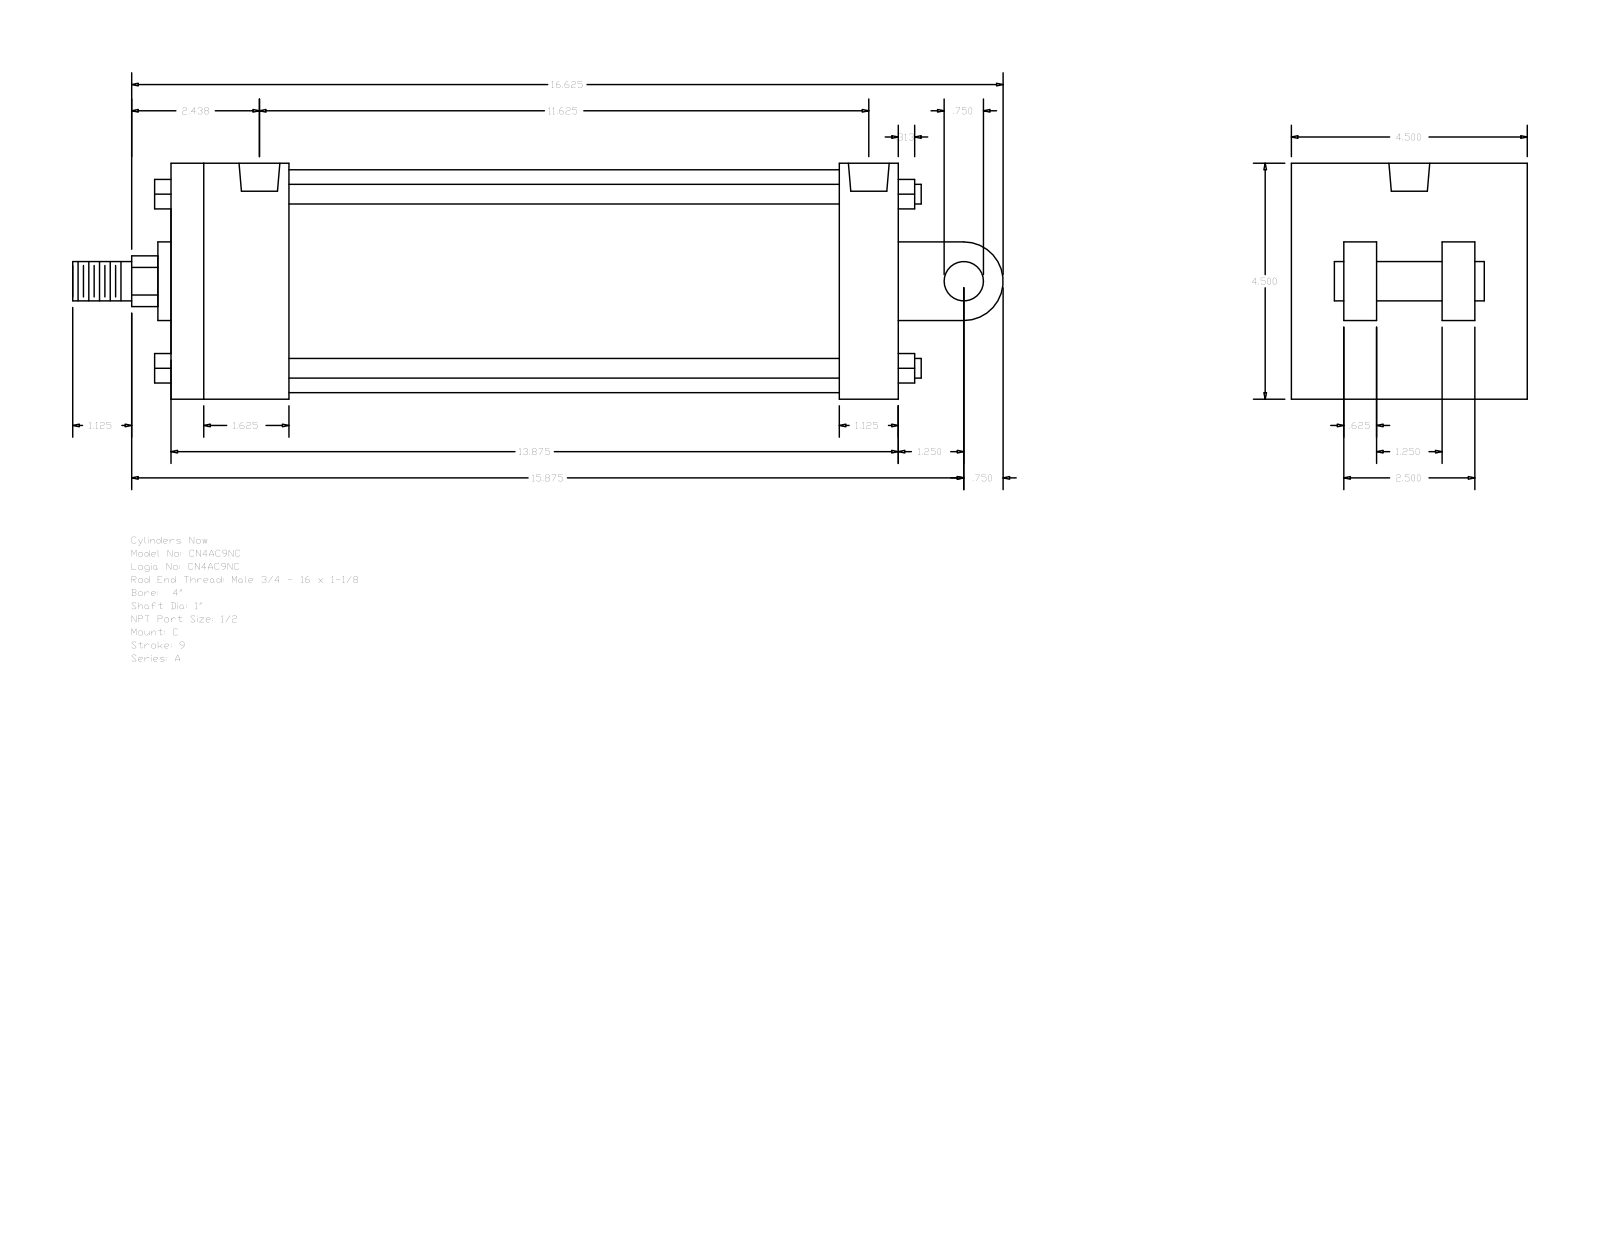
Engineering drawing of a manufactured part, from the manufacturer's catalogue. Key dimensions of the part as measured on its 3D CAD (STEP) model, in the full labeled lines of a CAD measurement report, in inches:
Part name (STEP PRODUCT): A_C__0400_1
STEP written by: GSSL Pune (CONFIG_CONTROL_DESIGN)
Units: inches
Bodies: 0 solids, 135 faces (102 planar, 33 cylindrical, 0 other)
Overall size (bounding box): 17.75 × 4.5 × 4.5
Round holes (diameter × count): ⌀0.344 ×4, ⌀0.778 ×2
Round bosses / shafts (diameter × count): ⌀0.375 ×4, ⌀0.75 ×2, ⌀4.25 ×1, ⌀1.5 ×1, ⌀1 ×1
Partial cylindrical surfaces — rounded edges, fillets, slot ends (radius × count): R0.484 ×1, R0.75 ×1
Main face-to-face distances: 4.5, 13.875, 2.875, 12.75, 1.125, 2.25, 10.5, 11.625, 1.625, 1.5
Hole centre spacings: 0.125, 11.375, 11.5, 11.625
